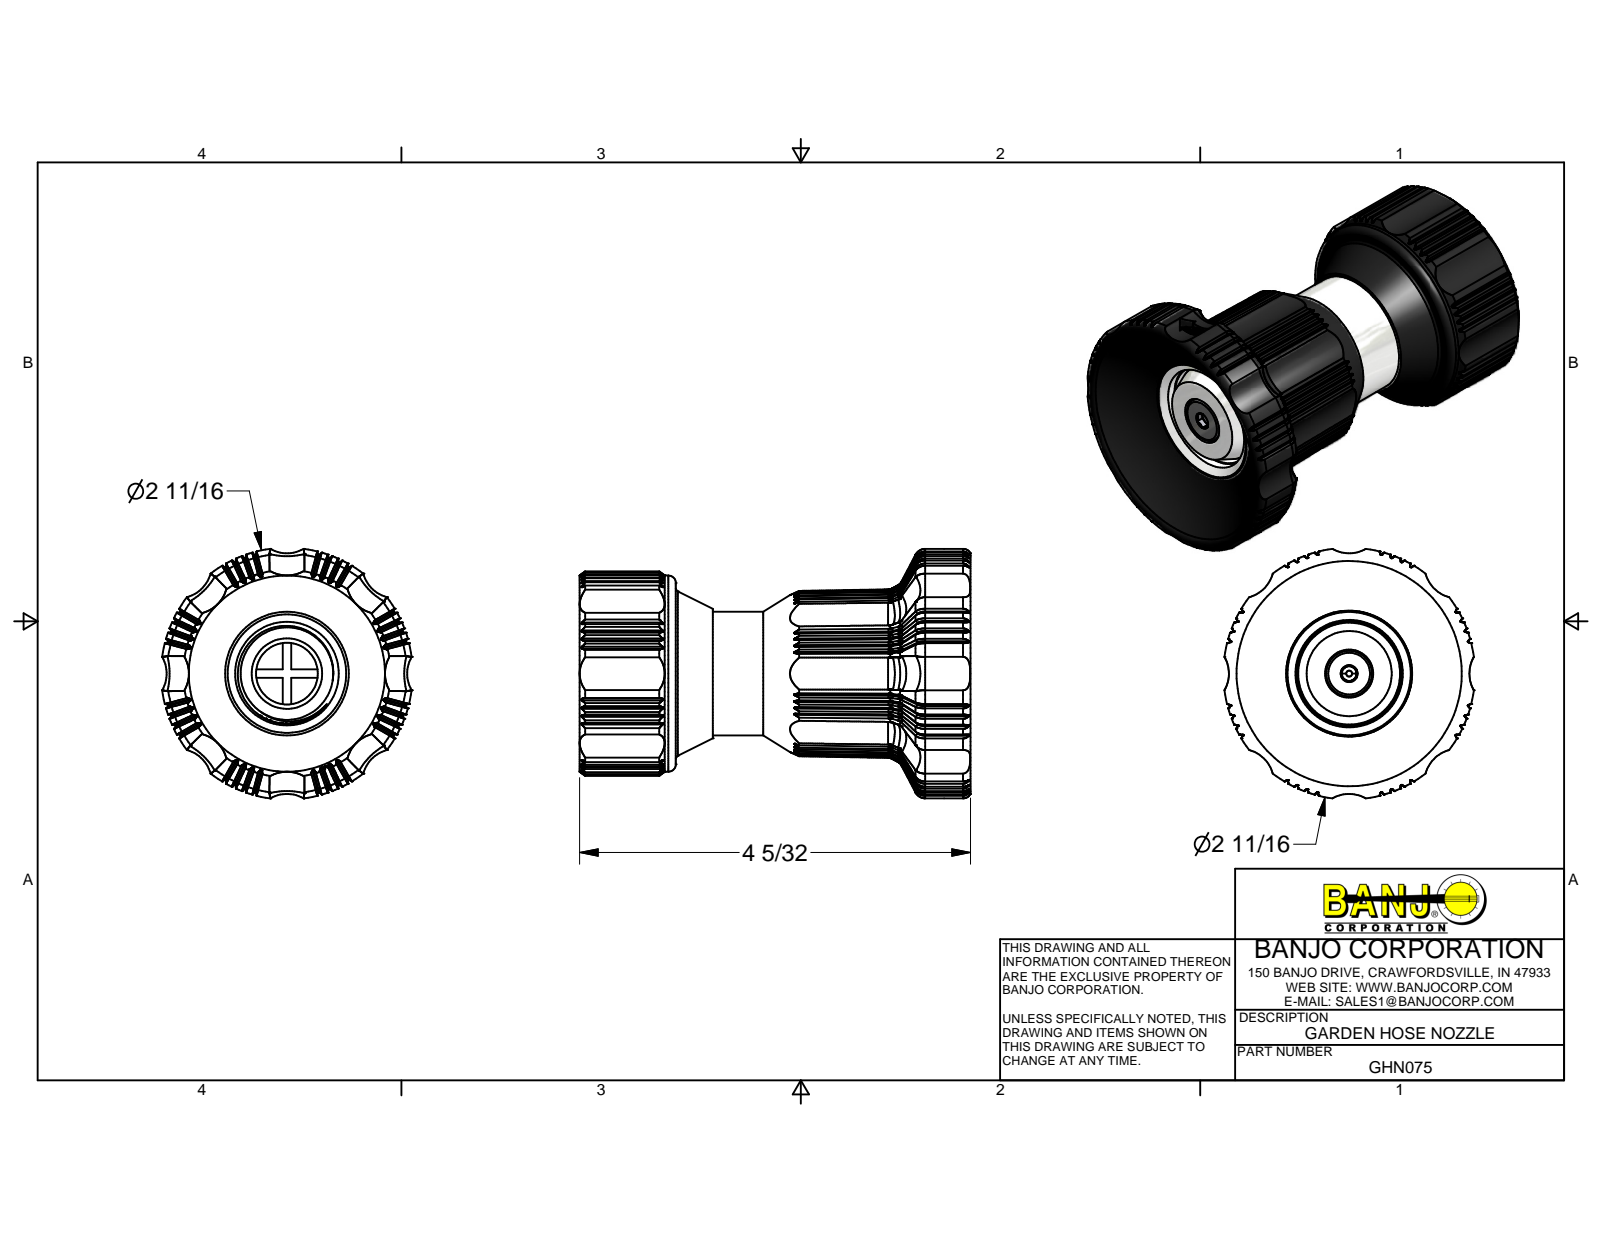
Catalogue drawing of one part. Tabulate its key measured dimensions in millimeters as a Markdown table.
| quantity | value |
| --- | --- |
| part name | GHN010; GHN01; GHN02; GHN03 (+7 more) |
| STEP written by | Autodesk Inventor 2014 (AUTOMOTIVE_DESIGN) |
| units | millimeters |
| bodies | 9 solids, 2039 faces (932 planar, 404 cylindrical, 703 other) |
| overall size | 105.6 × 68 × 68 |
| volume | 115 346 mm³ |
| surface area | 84 292 mm² |
| round holes (diameter × count) | 4.98 × 1, 6 × 1, 6.5 × 1, 13 × 1, 14 × 1, 19.05 × 1, 20 × 1, 24.7 × 1, 25 × 1, 27.3 × 1, 28.5 × 1, 28.6 × 1 |
| round bosses / shafts (diameter × count) | 5.39 × 6, 53 × 1, 34 × 1, 28 × 1, 27.78 × 1, 27.5 × 1, 24 × 1, 23 × 1 |
| partial cylindrical surfaces (radius × count) | 0.2 × 128, 9.08 × 40, 0.3 × 33, 0.4 × 12, 2.69 × 2, 14.08 × 1, 28 × 1, 34 × 1 |
| main face-to-face distances | 2, 7, 21, 23, 6.5, 4.5, 18.5, 11.5, 3, 87 |
